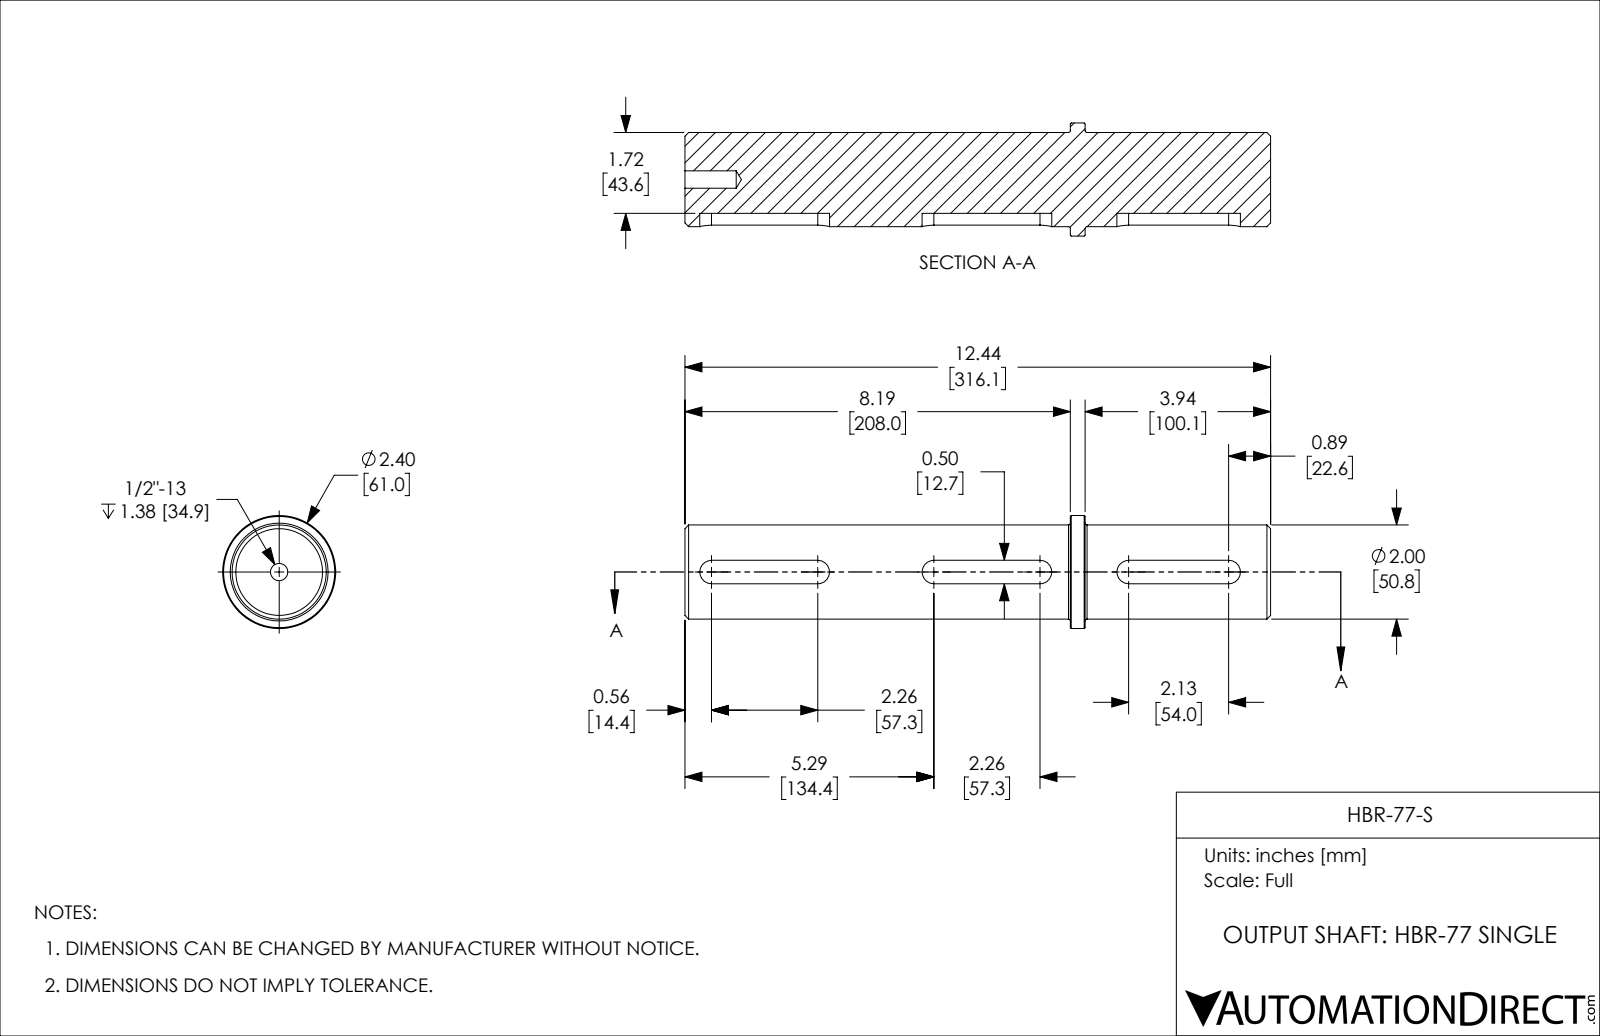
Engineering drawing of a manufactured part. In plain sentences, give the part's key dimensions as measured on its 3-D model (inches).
The part is named "HBR-77-S". Its 3-D file was written by "SolidWorks 2018 (AUTOMOTIVE_DESIGN)". It is 1 solid with 44 faces: 13 planar, 17 cylindrical and 14 other. Overall it measures 12.444 by 2.402 by 2.402 inches. Its volume is 38.31 cubic inches and its surface area 92.48 square inches. Round holes: 1 of diameter 0.368. Round bosses or shafts: 1 of diameter 2.402, 1 of diameter 2. Partial cylindrical surfaces (rounded edges, fillets, slot ends): 6 of radius 0.25. The main face-to-face distances are 12.444, 0.5, 8.189, 4.255, 8.504, 0.315, 3.94.
